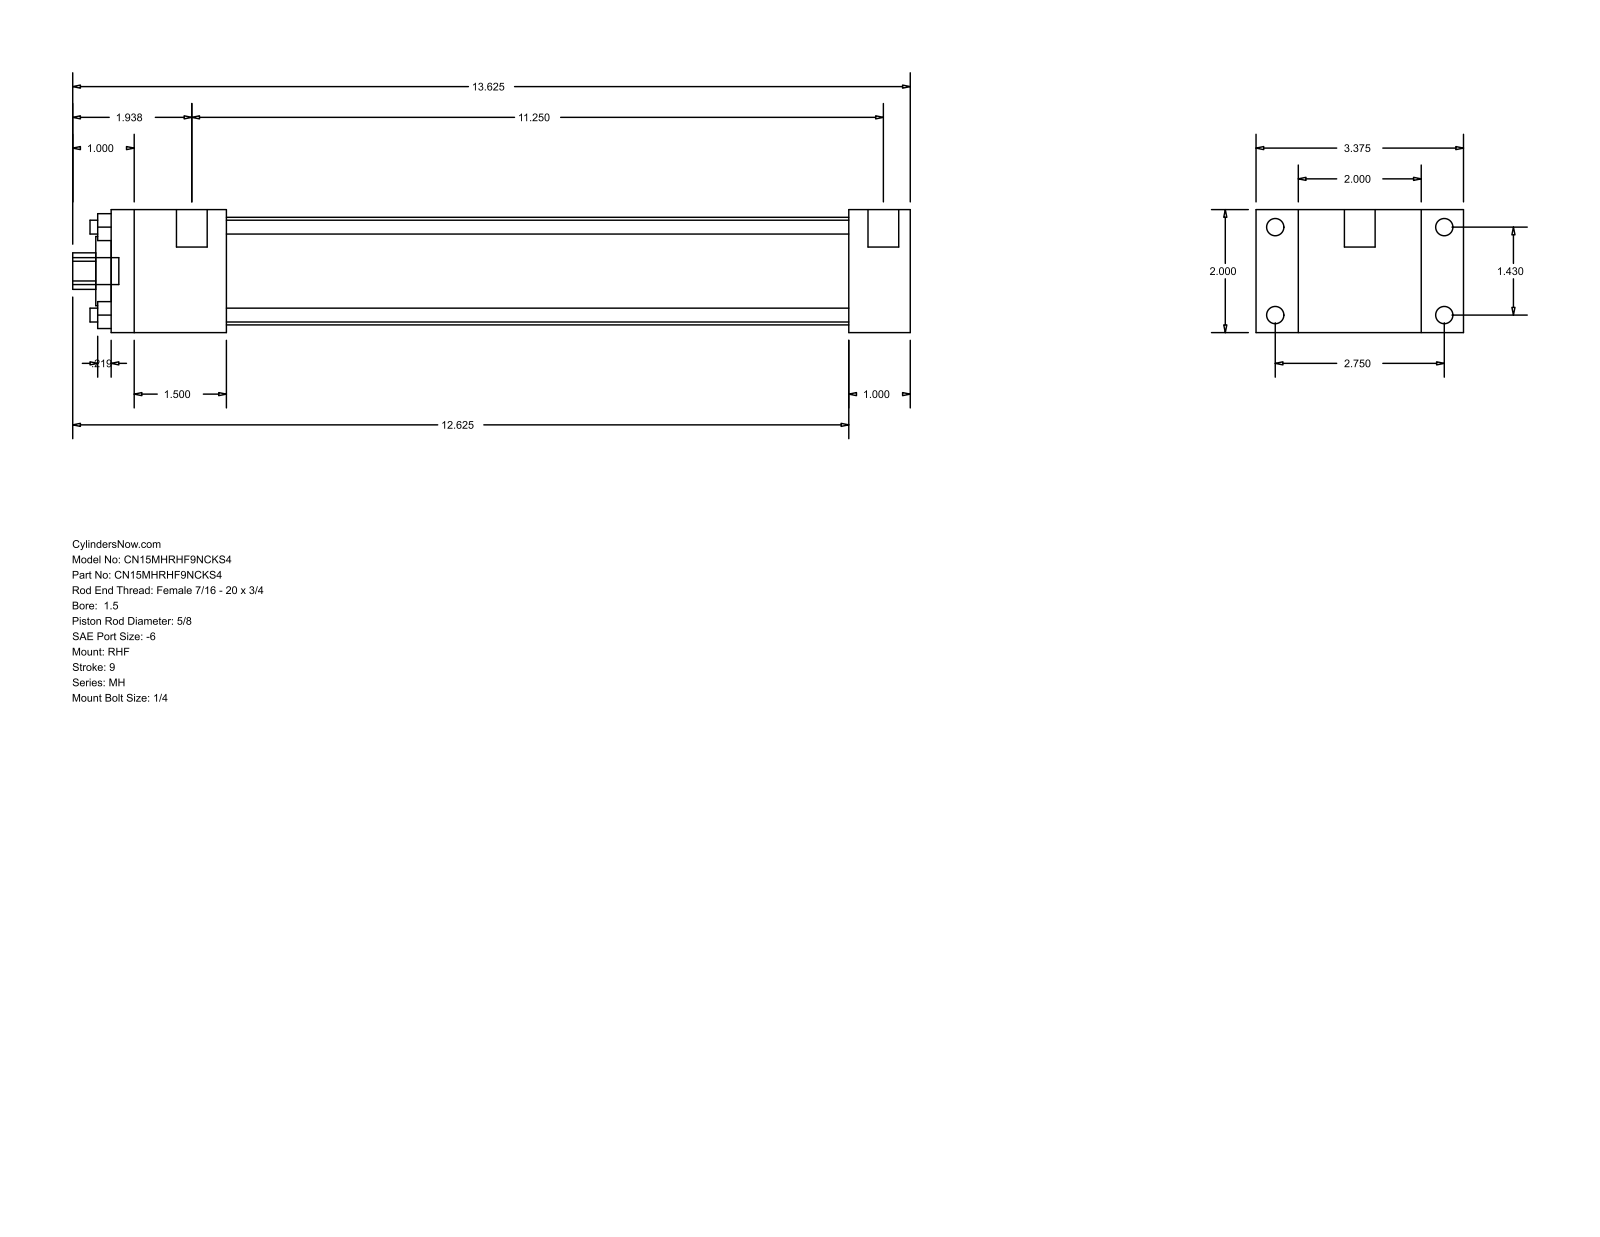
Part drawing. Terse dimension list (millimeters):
name: MH_RHF__0150_0.625
written by: GSSL Pune (CONFIG_CONTROL_DESIGN)
unit: mm
bodies: 0 solids, 88 faces (60 planar, 28 cylindrical, 0 other)
size: 346.07 × 85.72 × 50.8
holes: 4× ⌀5.71, 1× ⌀15.88, 1× ⌀28.57, 1× ⌀44.45
bosses: 4× ⌀7.14, 4× ⌀5.56, 2× ⌀12.7, 1× ⌀11.11
rounds: 1× R7.54
face distances: 50.8, 17.46, 68.26, 25.39, 304.8, 330.19, 85.72, 47.62, 257.18, 282.57
hole spacings: 25.68, 36.32, 51.36
